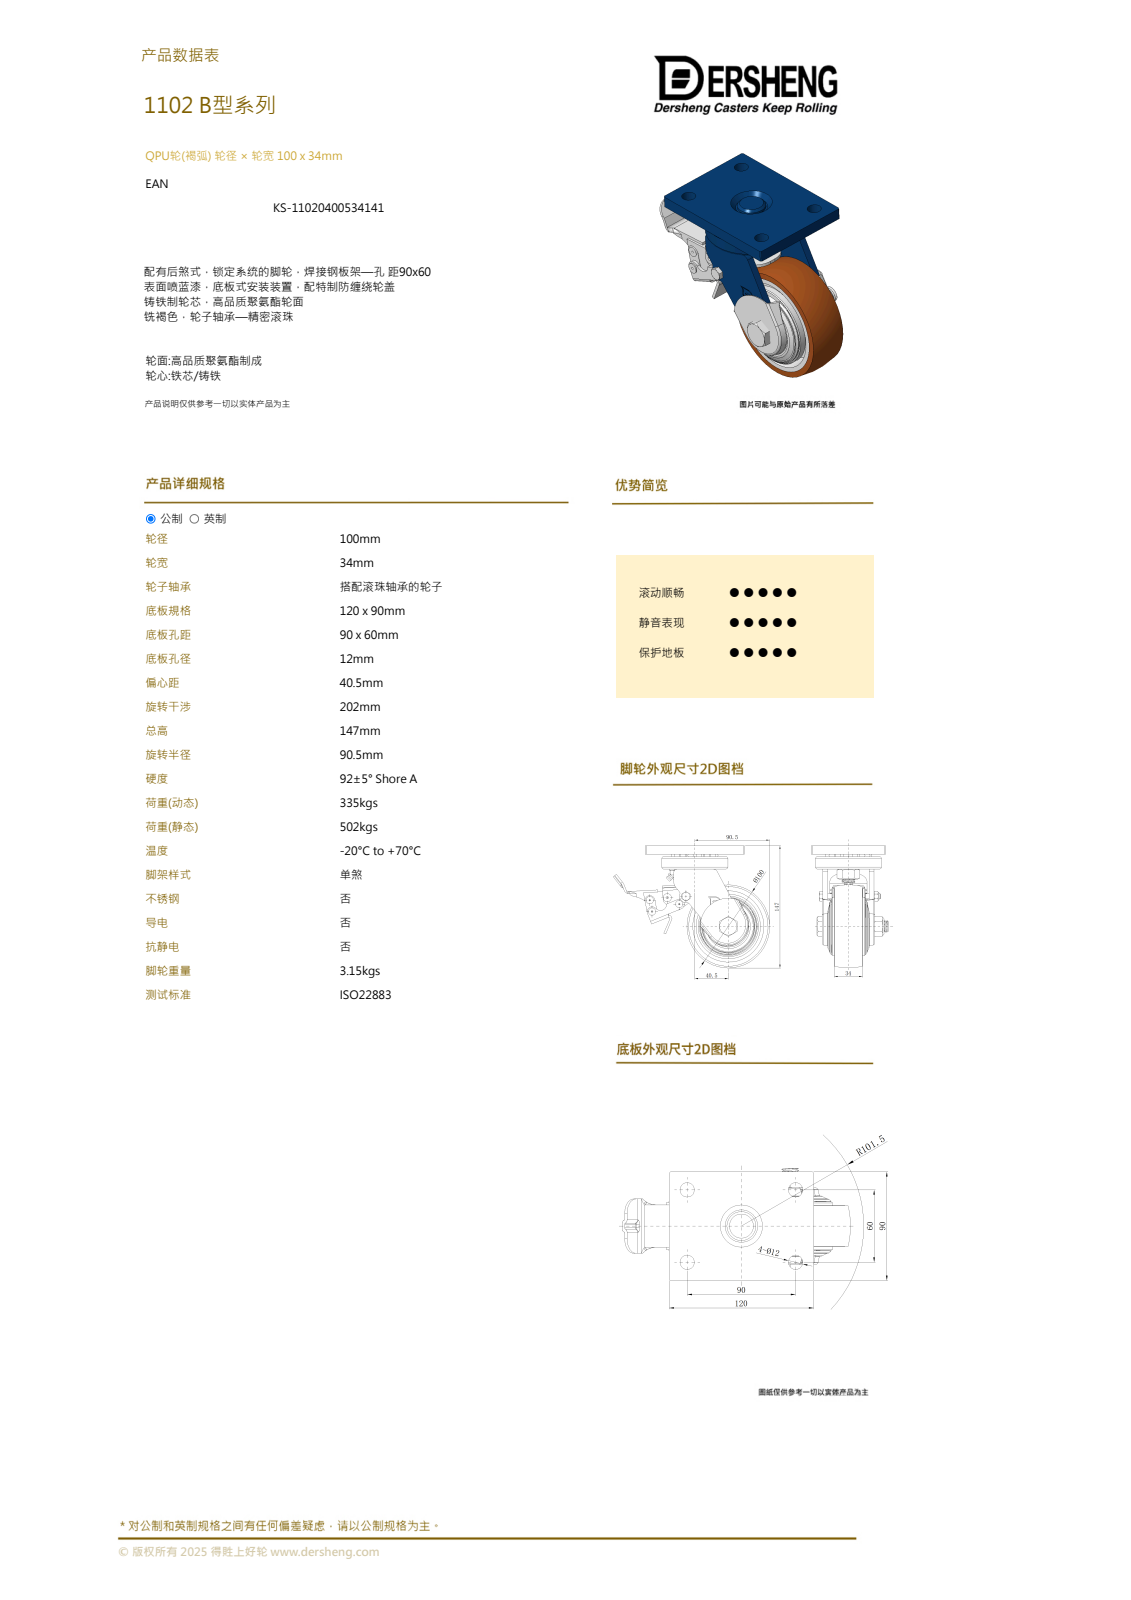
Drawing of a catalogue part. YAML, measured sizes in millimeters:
part_name: "110201060002"
step_written_by: "CREO PARAMETRIC BY PTC INC, 2022484 (CONFIG_CONTROL_DESIGN)"
units: millimeters
bodies: {solids: 0, faces: 565, planar: 192, cylindrical: 164, other: 209}
overall_size: [189.3, 147, 93]
round_holes:
  - {diameter: 12, count: 4}
  - {diameter: 30, count: 2}
  - {diameter: 31, count: 1}
  - {diameter: 68.6, count: 1}
round_bosses_or_shafts:
  - {diameter: 20, count: 2}
  - {diameter: 9, count: 2}
  - {diameter: 8, count: 2}
  - {diameter: 80, count: 1}
  - {diameter: 70, count: 1}
  - {diameter: 22, count: 1}
  - {diameter: 17, count: 1}
  - {diameter: 16, count: 1}
partial_cylinders:
  - {radius: 3, count: 10}
  - {radius: 1, count: 5}
  - {radius: 2, count: 5}
  - {radius: 6, count: 4}
  - {radius: 2.5, count: 3}
  - {radius: 1.3, count: 2}
  - {radius: 3.5, count: 2}
  - {radius: 4, count: 2}
face_to_face_distances: [56, 10, 6, 0.7, 14, 18, 62, 6.7, 28, 15]
hole_center_spacings: [54.08, 60, 90, 108.17]
